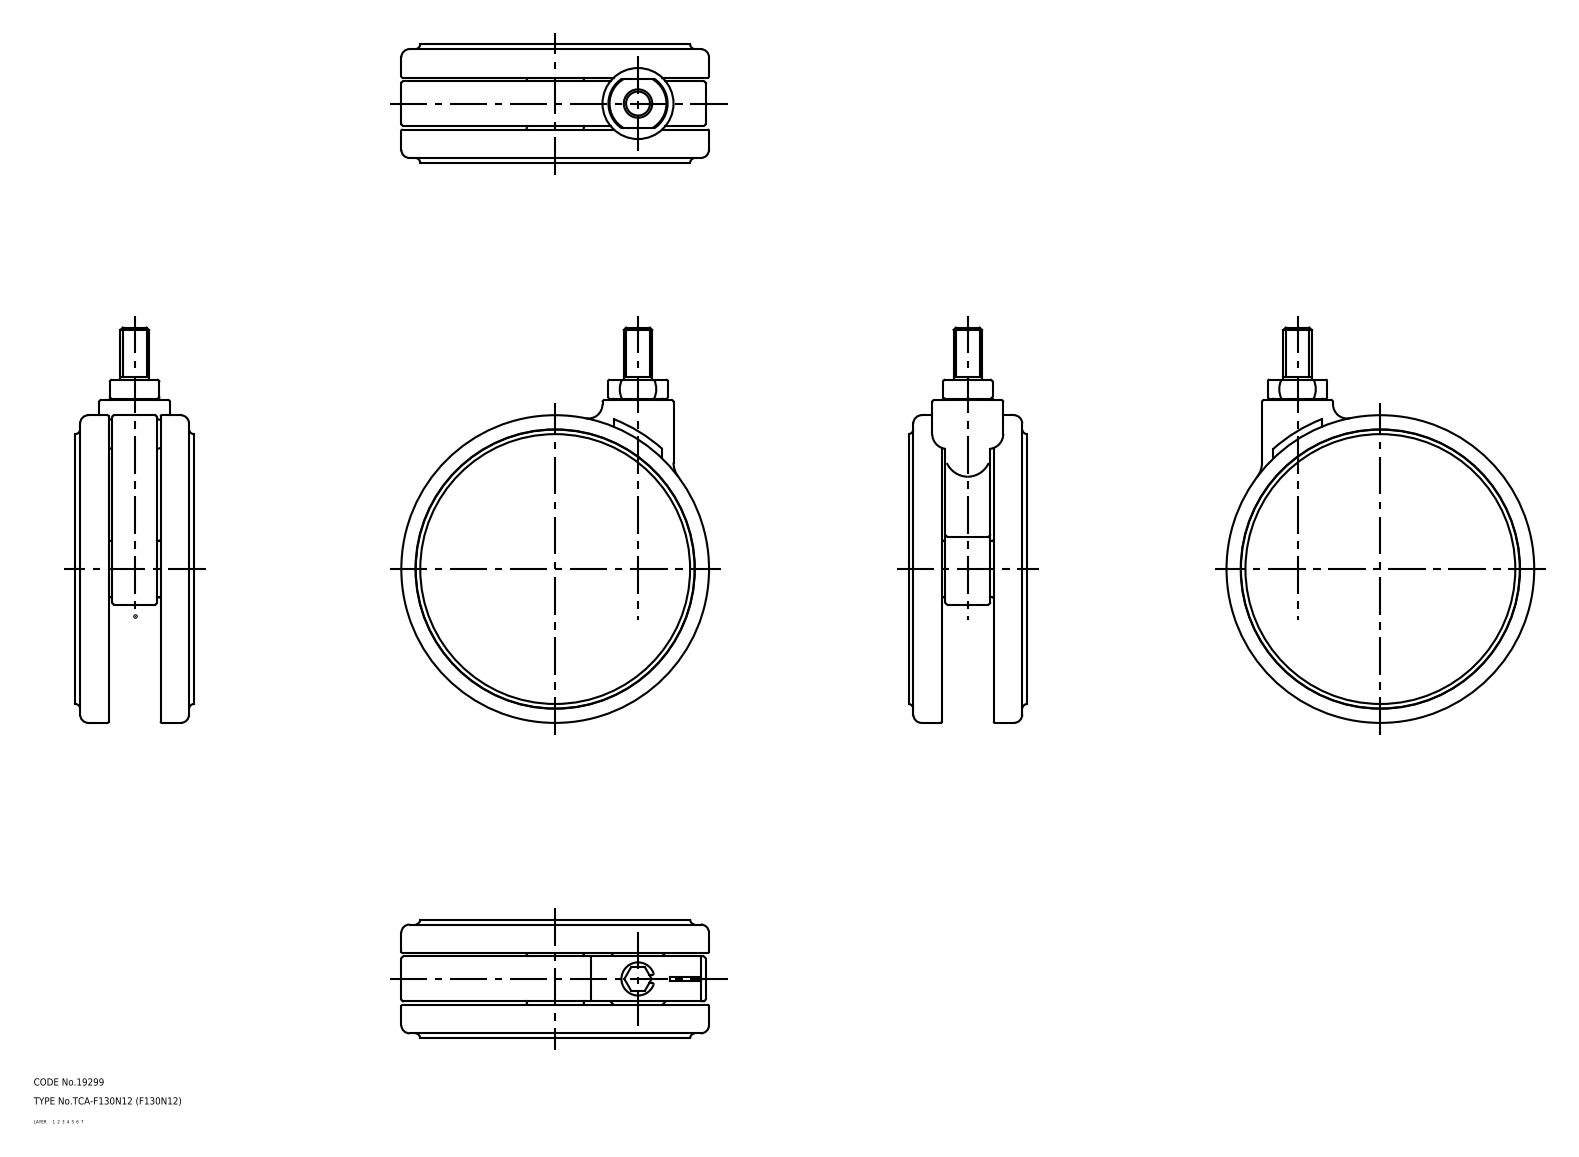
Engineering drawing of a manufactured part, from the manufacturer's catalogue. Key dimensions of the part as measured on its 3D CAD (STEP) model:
Part name (STEP PRODUCT): 67119600; 67119613; 67119626; 67119639
STEP written by: CADfix (AUTOMOTIVE_DESIGN)
Units: millimetres
Bodies: 4 solids, 148 faces (0 planar, 0 cylindrical, 148 other)
Overall size (bounding box): 167 × 130 × 50
Volume: 452 841 mm³ · Surface area: 92 209 mm²
